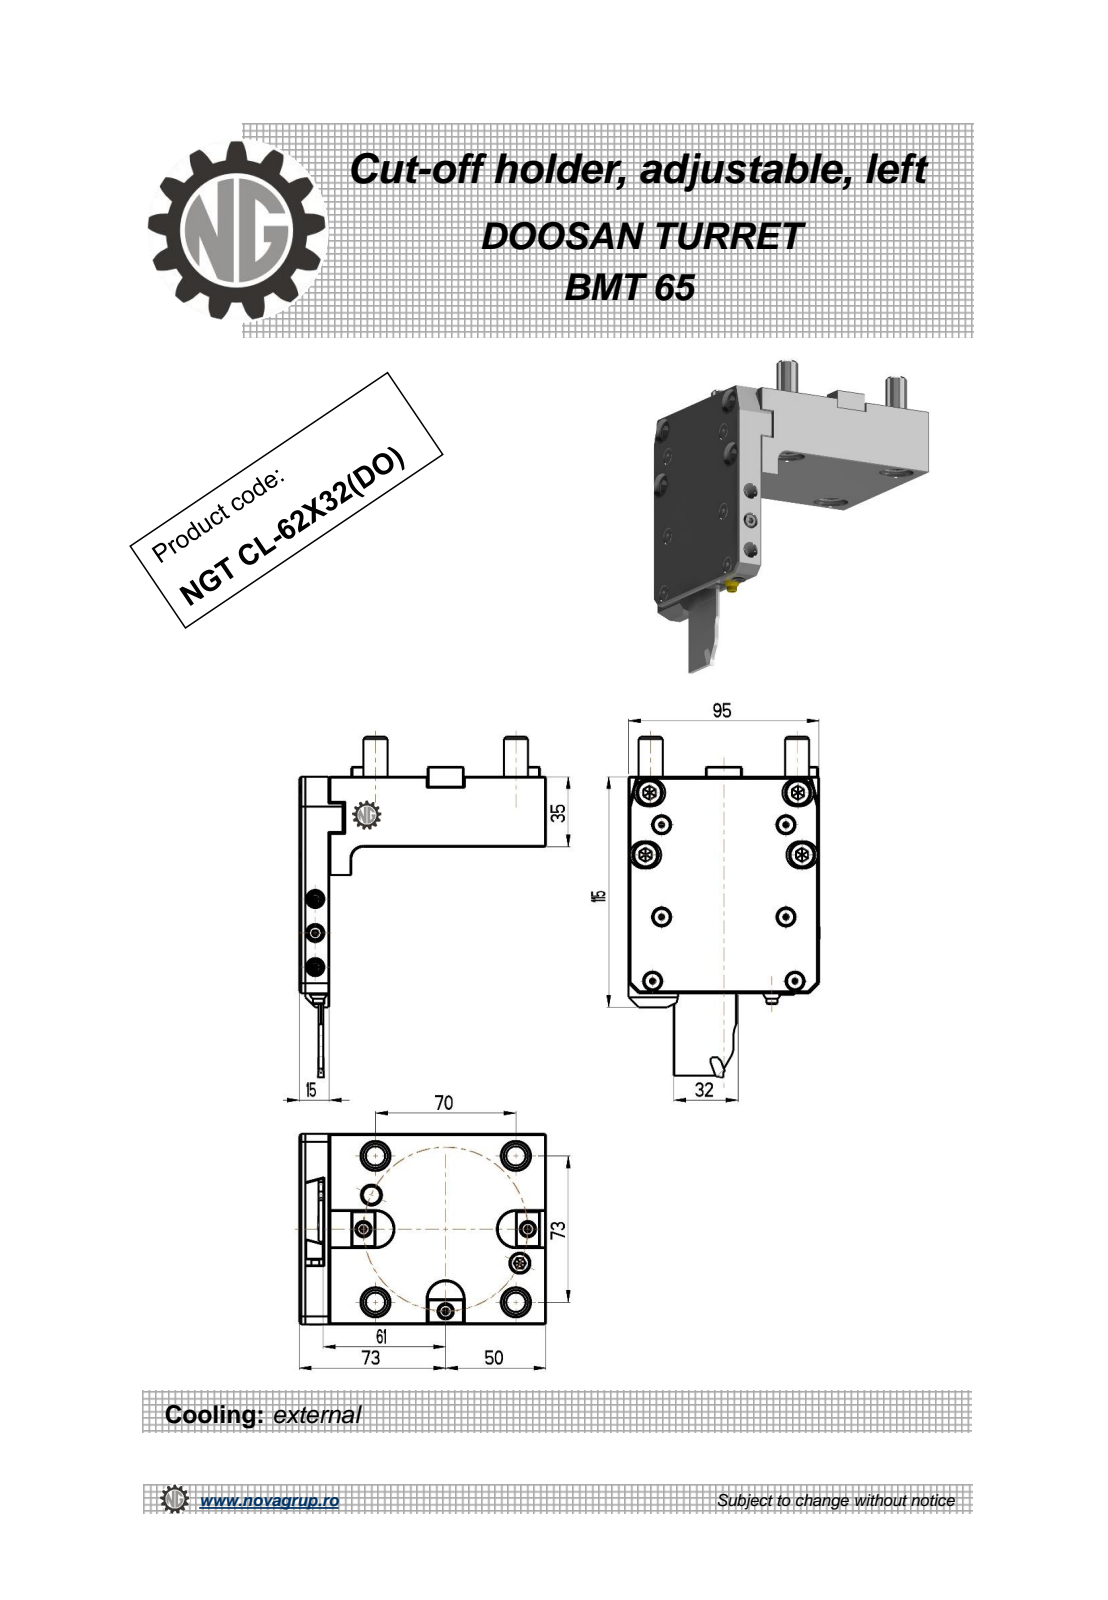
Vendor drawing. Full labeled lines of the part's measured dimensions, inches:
Part name (STEP PRODUCT): NGT_CL_65_32_DO
STEP written by: PRO/ENGINEER BY PARAMETRIC TECHNOLOGY CORPORATION, 2010280 (CONFIG_CONTROL_DESIGN)
Units: inches
Bodies: 1 solid, 438 faces (282 planar, 89 cylindrical, 67 other)
Overall size (bounding box): 5.315 × 4.843 × 3.745
Volume: 29.6 in³ · Surface area: 123.7 in²
Round holes (diameter × count): ⌀0.268 ×2, ⌀0.138 ×1, ⌀0.335 ×1
Round bosses / shafts (diameter × count): ⌀0.512 ×4, ⌀0.472 ×4, ⌀0.157 ×3, ⌀0.315 ×1, ⌀0.217 ×1
Partial cylindrical surfaces — rounded edges, fillets, slot ends (radius × count): R0.01 ×24, R0.266 ×8, R0.006 ×6, R0.006 ×6, R0.02 ×6, R0.354 ×3, R0.236 ×1, R2.362 ×1
Main face-to-face distances: 0.472, 0.118, 1.378, 0.591, 3.74, 0.354, 4.252, 4.724, 4.37, 4.843
Hole centre spacings: 1.922, 3.071
